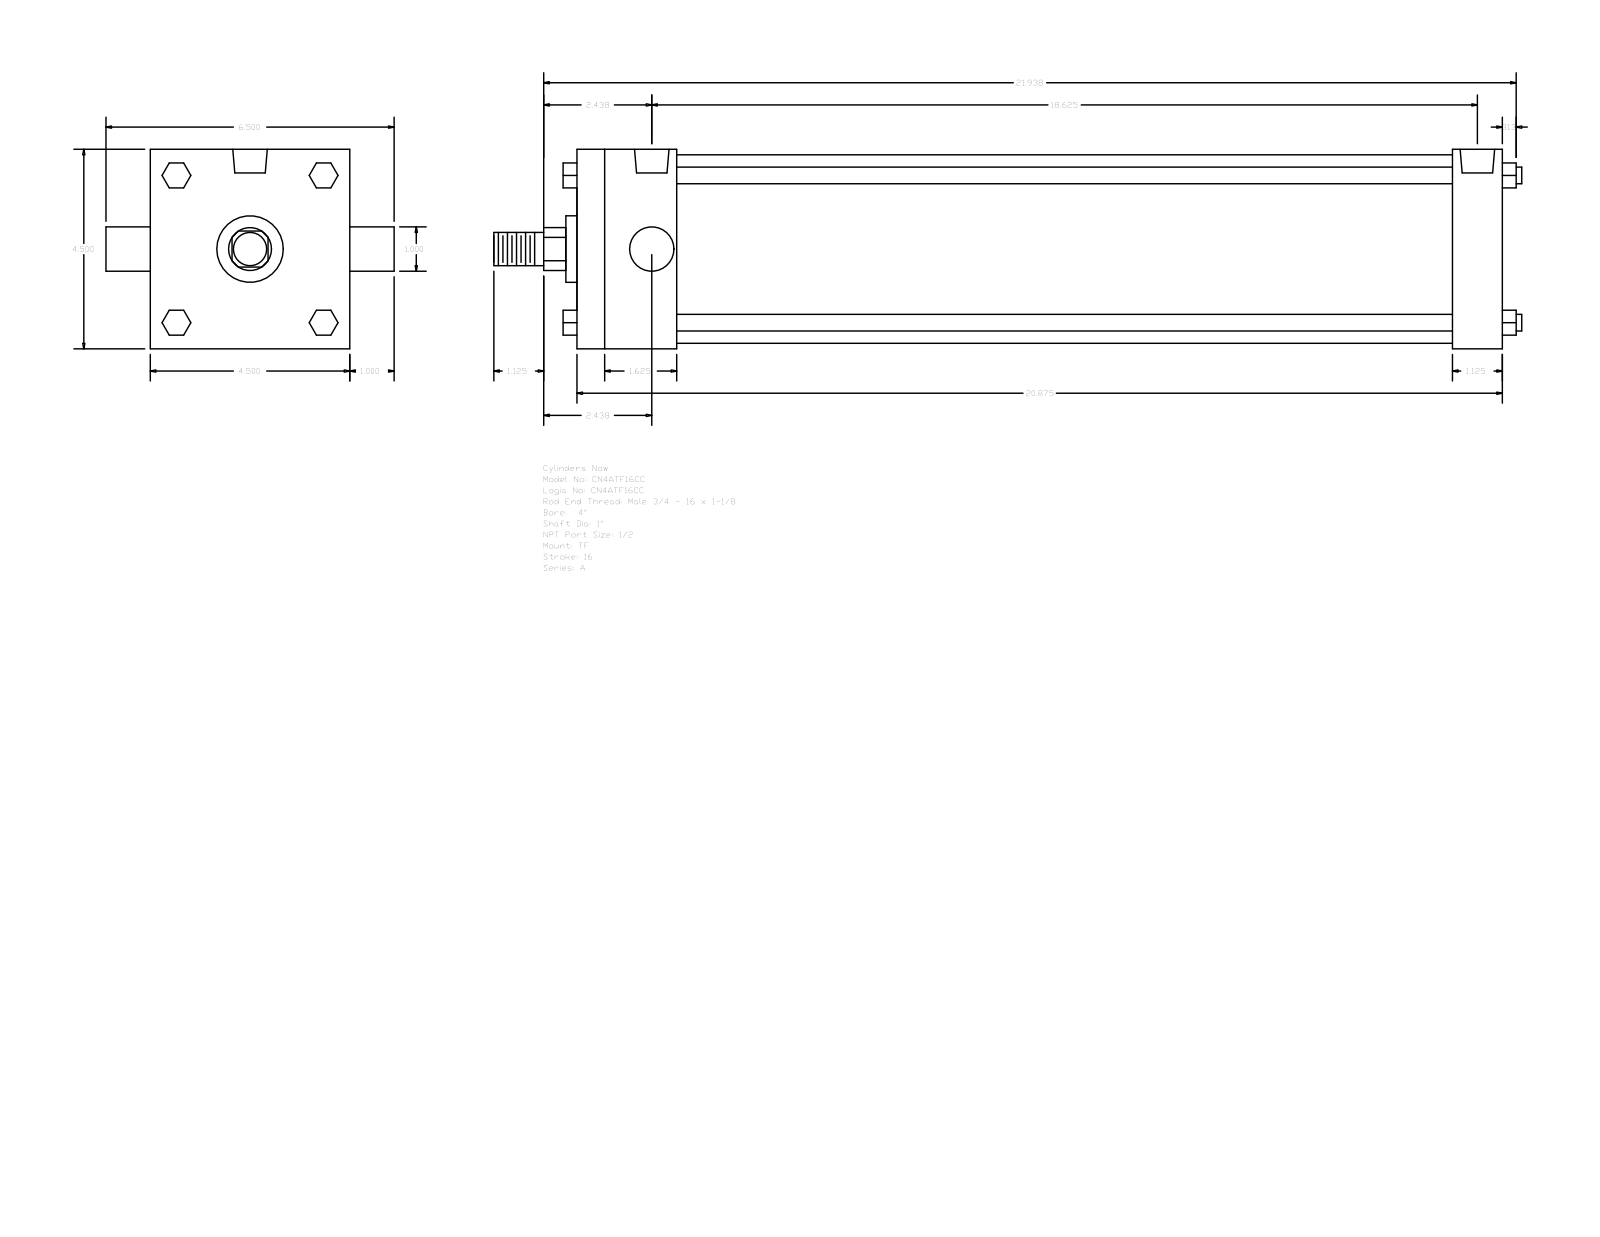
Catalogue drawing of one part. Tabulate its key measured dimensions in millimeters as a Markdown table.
| quantity | value |
| --- | --- |
| part name | A_TF__0400_1 |
| STEP written by | GSSL Pune (CONFIG_CONTROL_DESIGN) |
| units | millimeters |
| bodies | 0 solids, 120 faces (92 planar, 28 cylindrical, 0 other) |
| overall size | 588.96 × 165.1 × 114.3 |
| round holes (diameter × count) | 8.73 × 3, 19.77 × 2 |
| round bosses / shafts (diameter × count) | 9.53 × 4, 25.4 × 2, 107.95 × 1, 38.1 × 1, 19.05 × 1 |
| partial cylindrical surfaces (radius × count) | 12.29 × 1 |
| main face-to-face distances | 114.3, 530.22, 28.57, 501.65, 57.15, 444.5, 473.07, 14.29, 42.16, 73.03 |
| hole center spacings | 3.18, 469.9, 466.72, 473.08 |
